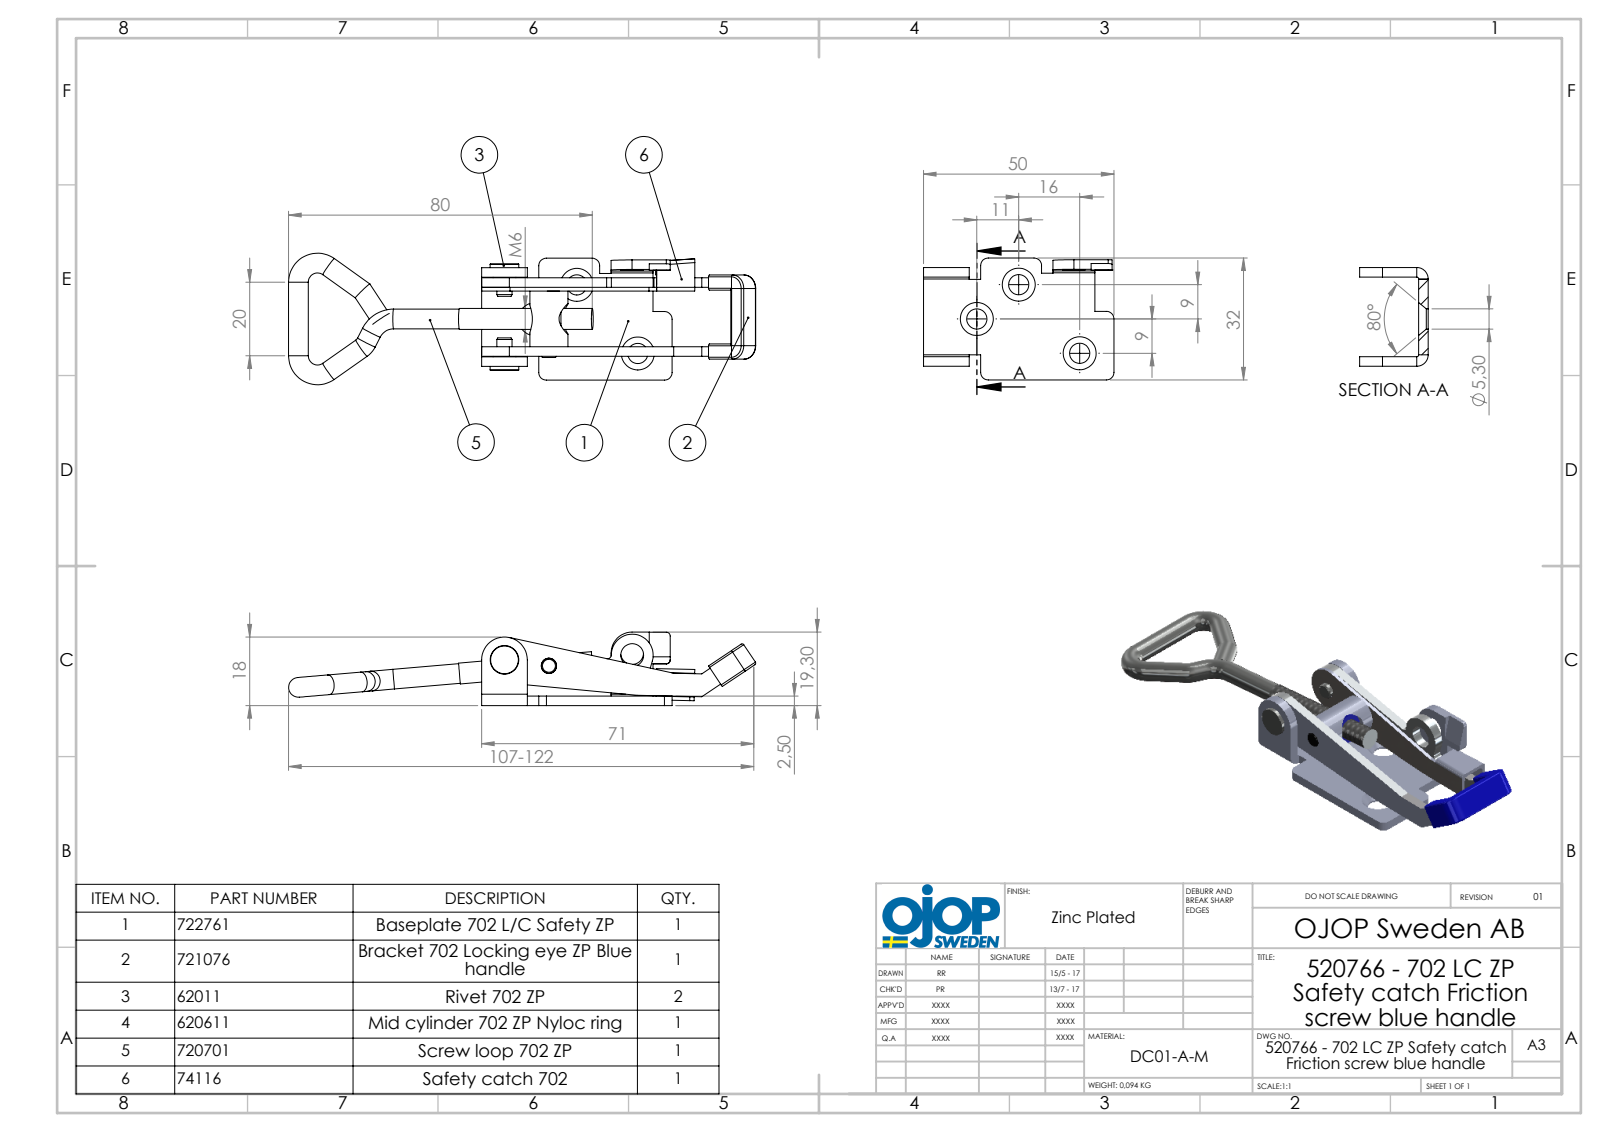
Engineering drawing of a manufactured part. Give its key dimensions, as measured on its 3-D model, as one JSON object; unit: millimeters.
{"part_name": "702 - Platta LC Spärr; 702 - Bygel låsögla blåplast; 702 - Ansatsnit; 702 - Rulle Friktion (+5 more)", "step_written_by": "SolidWorks 2015 (AUTOMOTIVE_DESIGN)", "units": "millimeters", "bodies": {"solids": 8, "faces": 262, "planar": 107, "cylindrical": 115, "other": 40}, "overall_size": [122.2, 34.52, 19.3], "volume_mm3": 12807, "surface_area_mm2": 13246, "round_holes": [[5.3, 3], [6, 3], [4, 2], [4.1, 2], [5, 1], [5.1, 1], [8, 1]], "round_bosses_or_shafts": [[5.18, 6], [10, 1], [7.5, 1], [5.5, 1]], "partial_cylinders_radius": [[0.5, 15], [1, 11], [2, 5], [3, 3], [0.45, 2], [3.55, 2], [5.5, 2], [6, 1]], "face_to_face_distances": [2.5, 18.1, 1, 20.75, 3.5, 15.6, 2.65, 20.6, 14.6, 17.1], "hole_center_spacings": [11.77, 14.21, 22.04, 24.08, 28.46, 33.55]}
